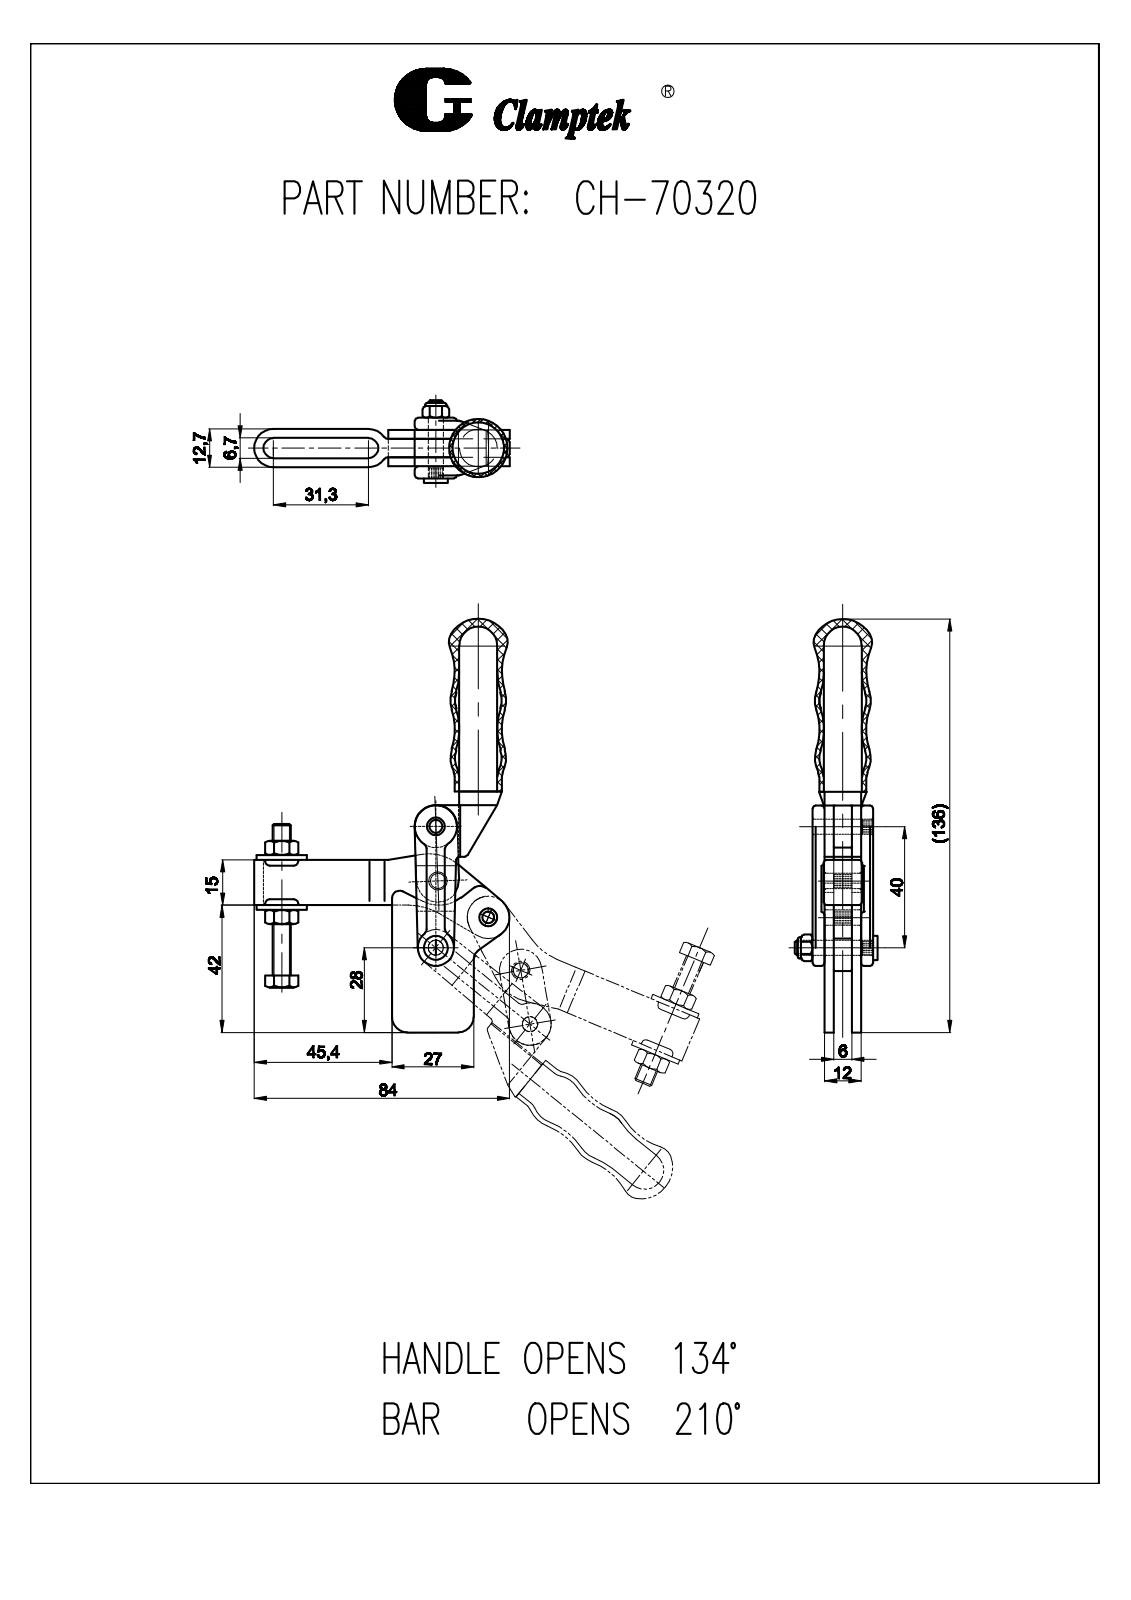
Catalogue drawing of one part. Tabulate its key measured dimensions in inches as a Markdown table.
| quantity | value |
| --- | --- |
| part name | ёфМЧ; CH-FW-141; hex nuts, style 2-grades ab gb_GB_HEXAGON_TYPE13 M6 Normal Style-N; ВЭёЛ (+2 more) |
| STEP written by | SolidWorks 2015 (CONFIG_CONTROL_DESIGN) |
| units | inches |
| bodies | 18 solids, 1267 faces (343 planar, 303 cylindrical, 621 other) |
| overall size | 5.294 × 3.328 × 1.043 |
| volume | 2.496 in³ |
| surface area | 49 in² |
| round holes (diameter × count) | 0.197 × 4, 0.194 × 2, 0.268 × 2, 0.066 × 1, 0.163 × 1, 0.205 × 1, 0.493 × 1, 0.493 × 1 |
| round bosses / shafts (diameter × count) | 0.203 × 4, 0.61 × 1, 0.551 × 1, 0.461 × 1, 0.315 × 1, 0.306 × 1, 0.236 × 1, 0.065 × 1 |
| partial cylindrical surfaces (radius × count) | 0.039 × 17, 0.059 × 6, 0.118 × 2, 0.132 × 2, 0.197 × 2, 0.25 × 2, 0.276 × 2, 0.327 × 2 |
| main face-to-face distances | 0.118, 0.354, 0.236, 0.472, 0.014, 0.368, 0.157, 0.512, 0.144, 0.526 |
| hole center spacings | 0.676, 0.709, 0.787, 0.807, 0.867, 1.362, 1.371, 1.527 |
